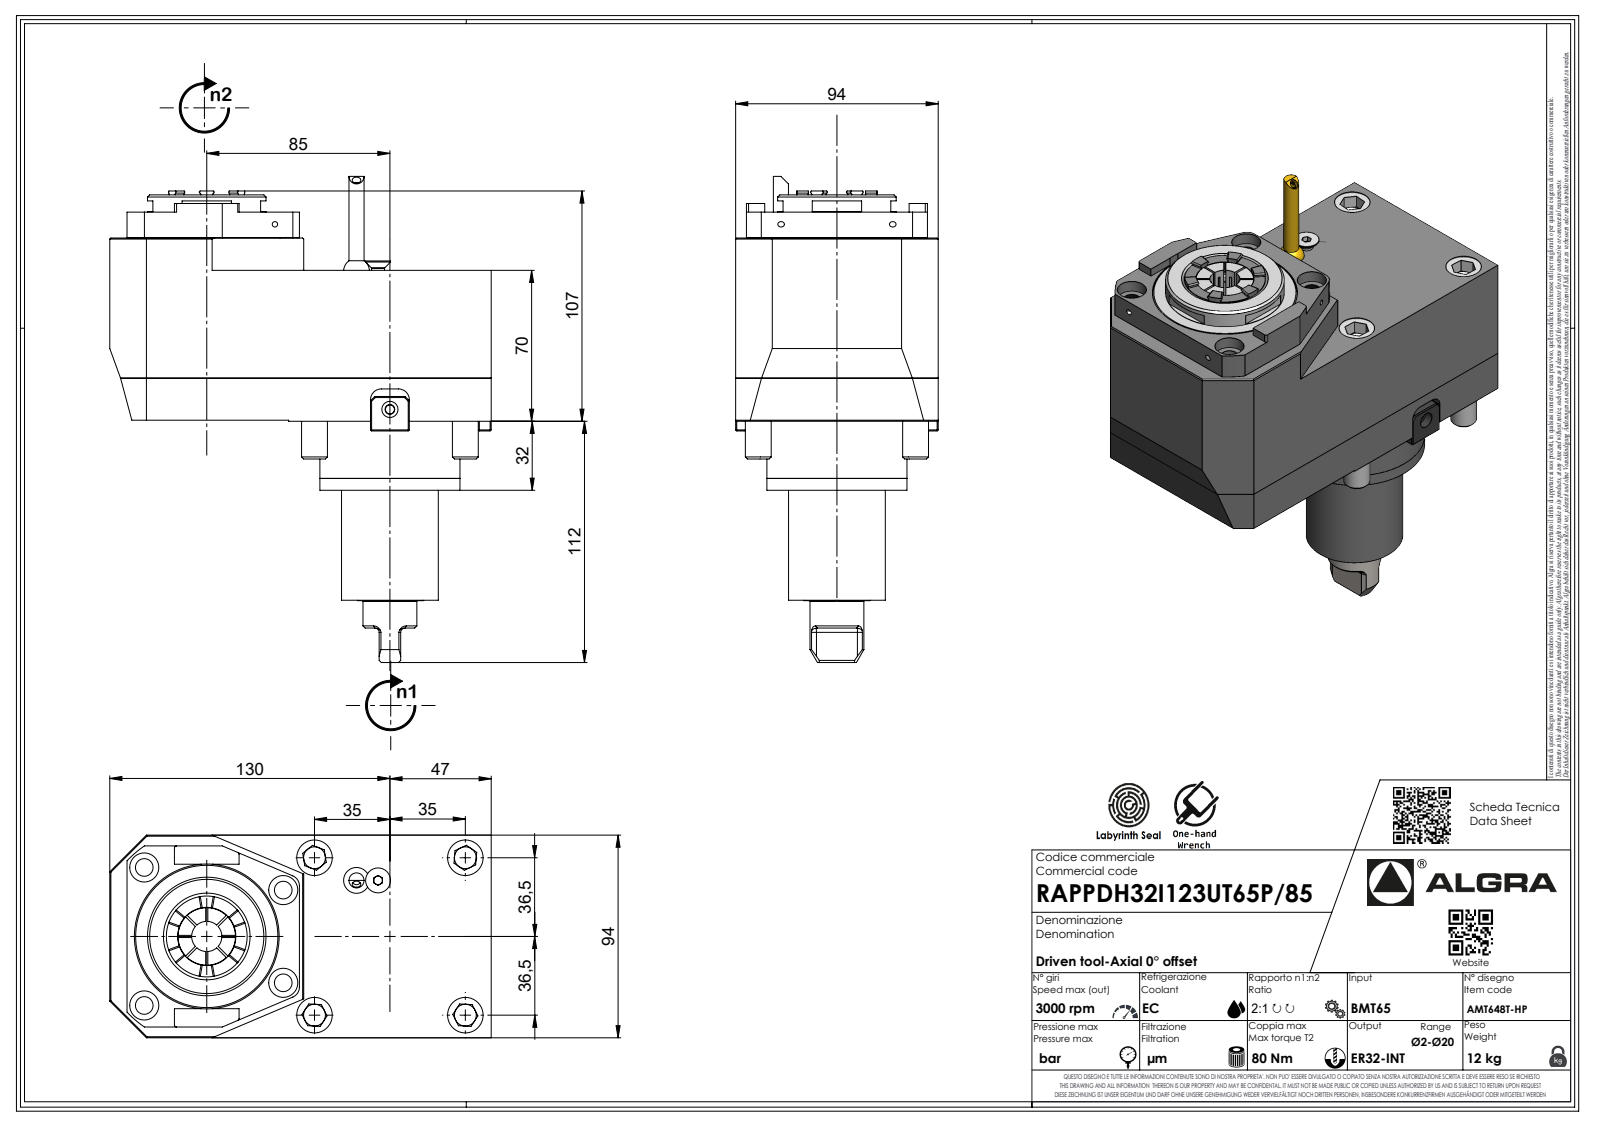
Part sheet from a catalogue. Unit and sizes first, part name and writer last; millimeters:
Units: millimetres
Overall size (bounding box): 225.47 × 177 × 94
Round holes (diameter × count): ⌀4 ×1, ⌀4.2 ×1
Round bosses / shafts (diameter × count): ⌀12 ×4, ⌀65 ×1, ⌀55 ×1, ⌀45 ×1, ⌀44.9 ×1, ⌀25 ×1, ⌀23.2 ×1, ⌀12.73 ×1
Partial cylindrical surfaces — rounded edges, fillets, slot ends (radius × count): R0.67 ×7, R1.04 ×7, R2 ×7, R7.41 ×7, R5 ×6, R1 ×4, R0.42 ×1, R13.5 ×1
Main face-to-face distances: 94, 69.5, 15, 84.5, 70, 0.5, 85, 85.1, 84.6, 15.1
Volume: 1 539 000 mm³ · Surface area: 109 489 mm²
Bodies: 1 solid, 646 faces (404 planar, 75 cylindrical, 167 other)
Part name (STEP PRODUCT): RAPPDH32I123UT65P85
STEP written by: SolidWorks 2023 (AUTOMOTIVE_DESIGN)
